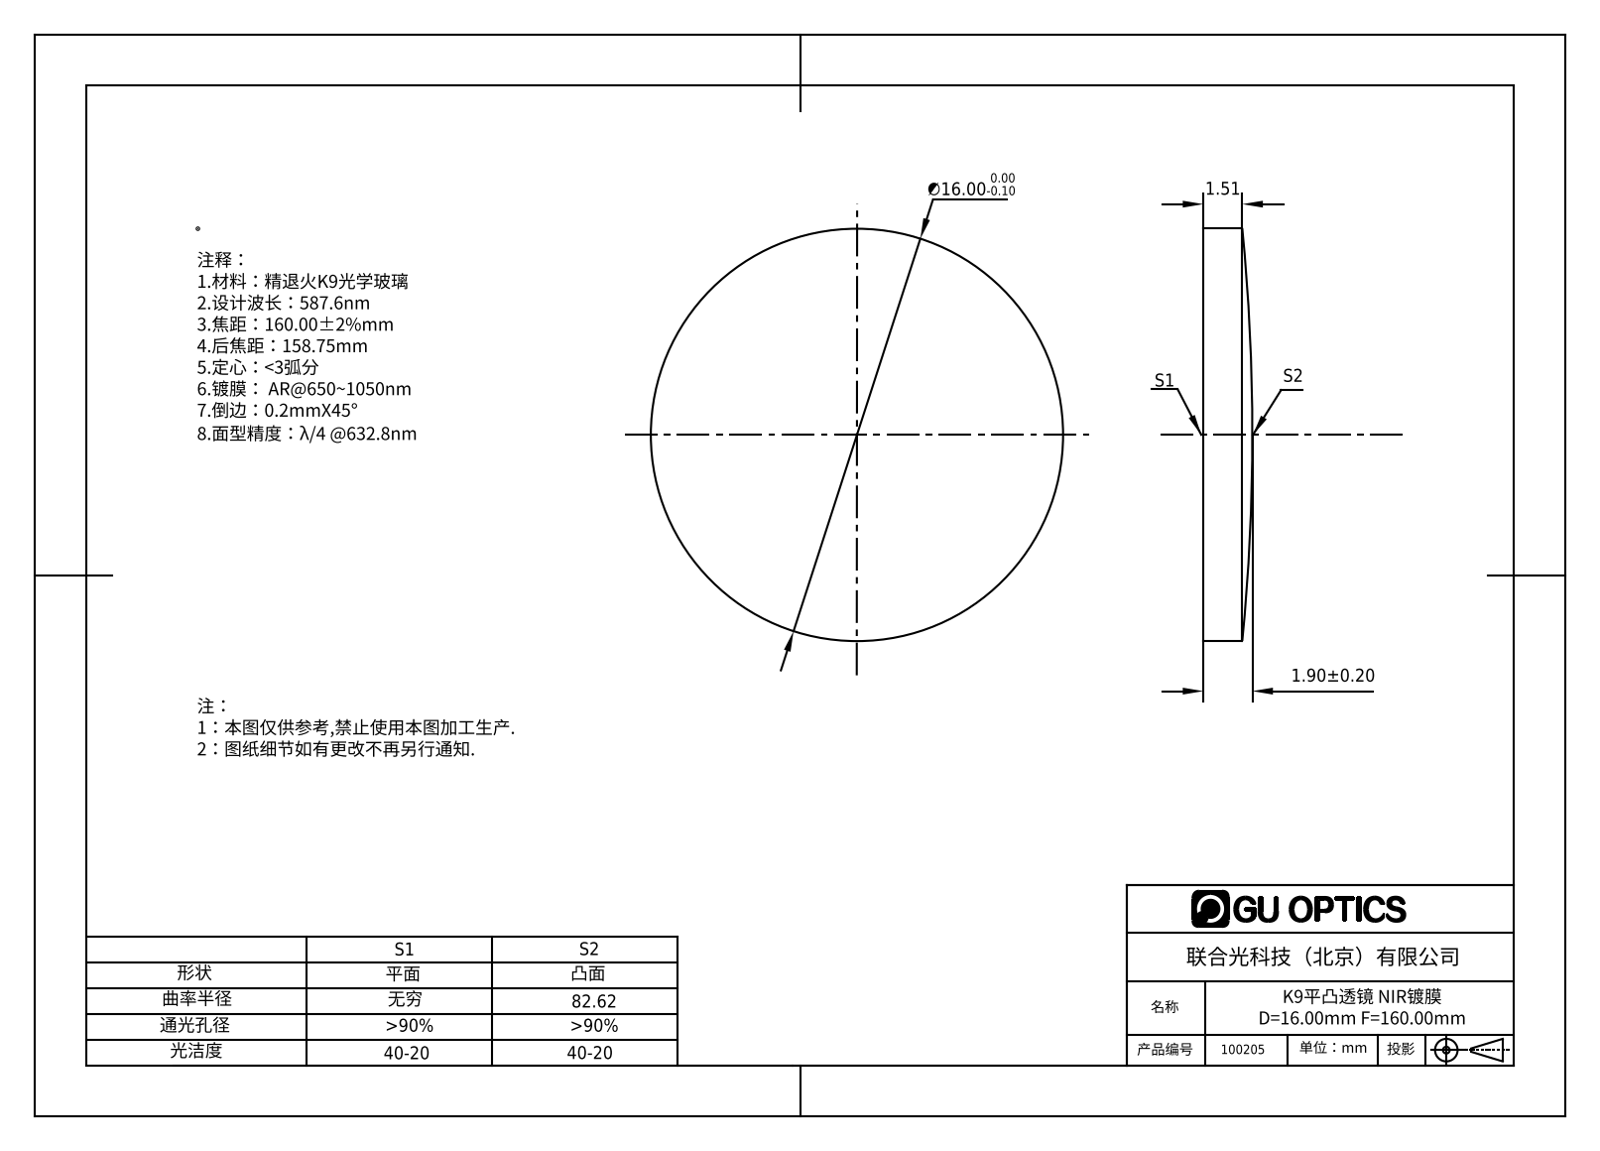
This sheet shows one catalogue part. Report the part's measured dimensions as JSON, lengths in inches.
{"part_name": "100205", "step_written_by": "SolidWorks 2016 (AUTOMOTIVE_DESIGN)", "units": "inches", "bodies": {"solids": 1, "faces": 5, "planar": 1, "cylindrical": 2, "other": 2}, "overall_size": [1.575, 1.575, 0.187], "volume_in3": 0.327, "surface_area_in2": 4.636, "round_bosses_or_shafts": [[1.575, 1]]}
